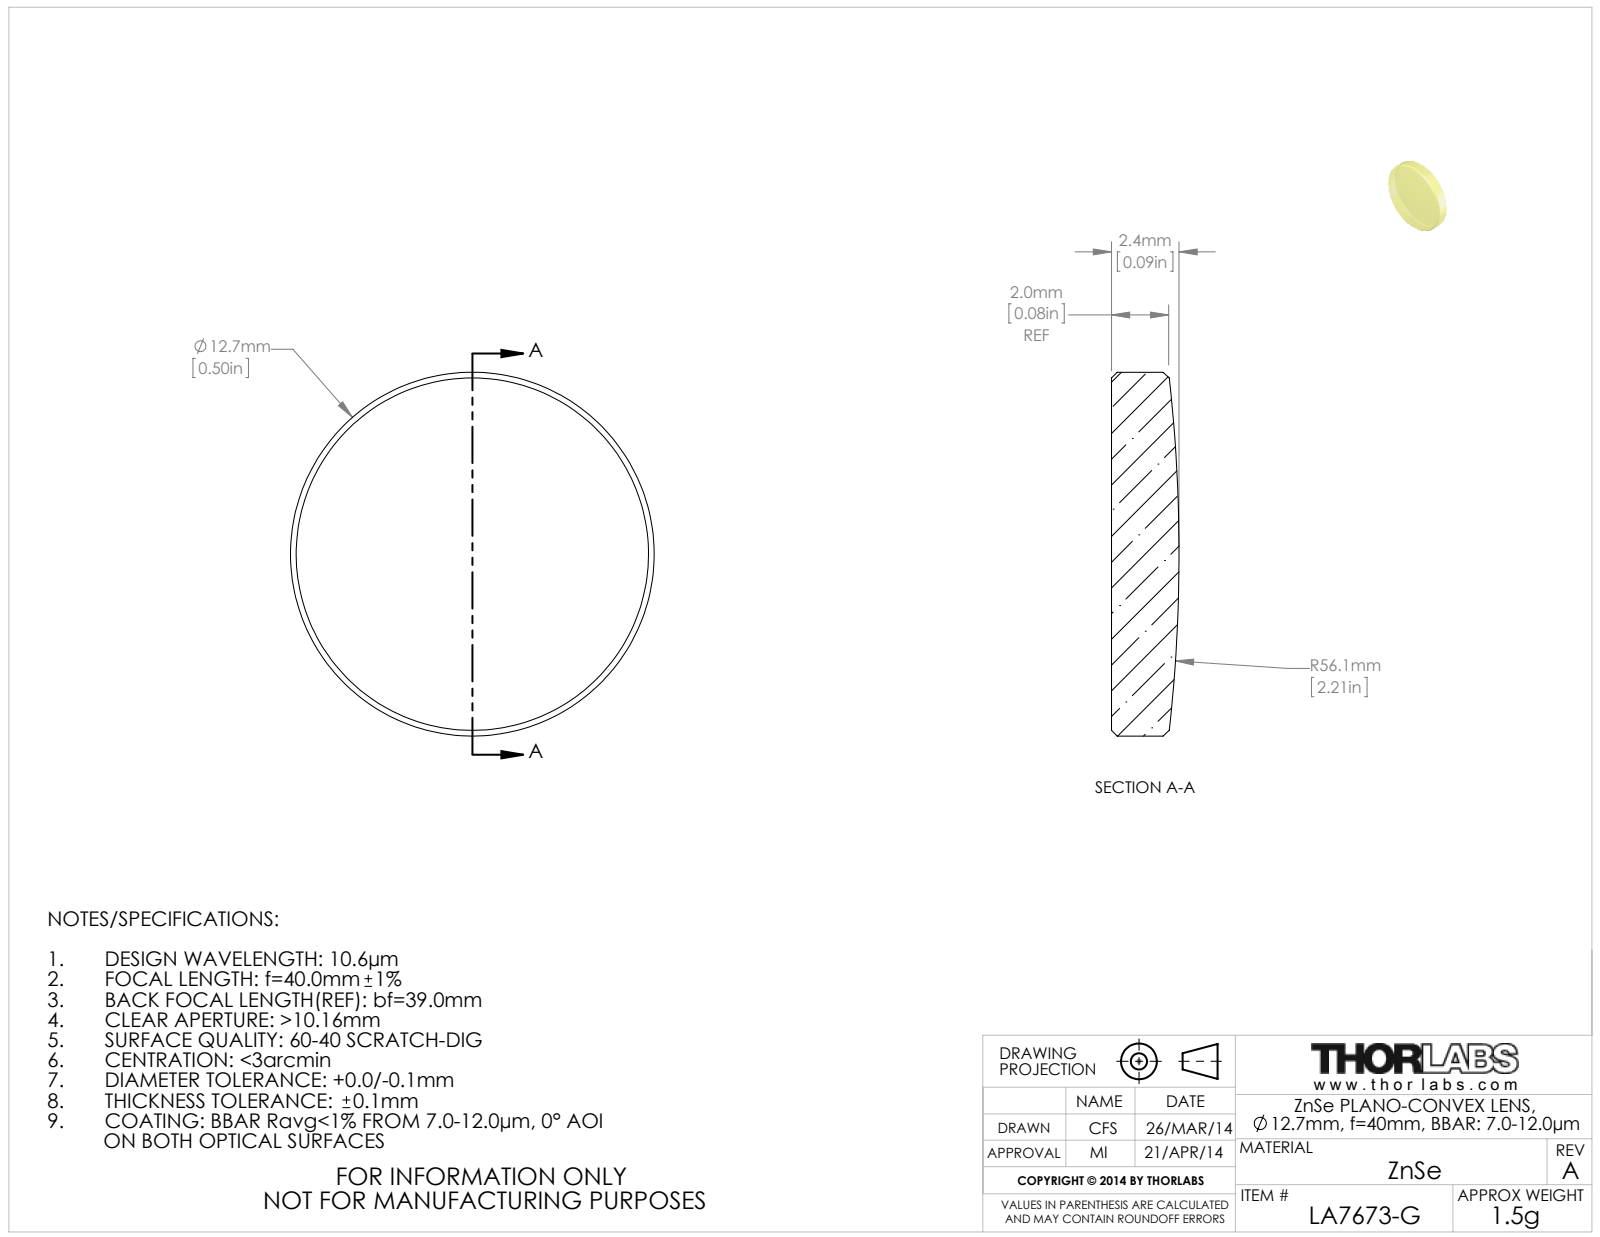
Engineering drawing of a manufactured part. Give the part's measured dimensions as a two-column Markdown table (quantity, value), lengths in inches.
| quantity | value |
| --- | --- |
| part name | TTN023911-E0W |
| STEP written by | SolidWorks 2012 (CONFIG_CONTROL_DESIGN) |
| units | inches |
| bodies | 1 solid, 9 faces (1 planar, 2 cylindrical, 6 other) |
| overall size | 0.5 × 0.5 × 0.093 |
| volume | 0.017 in³ |
| surface area | 0.503 in² |
| round bosses / shafts (diameter × count) | 0.5 × 1 |
